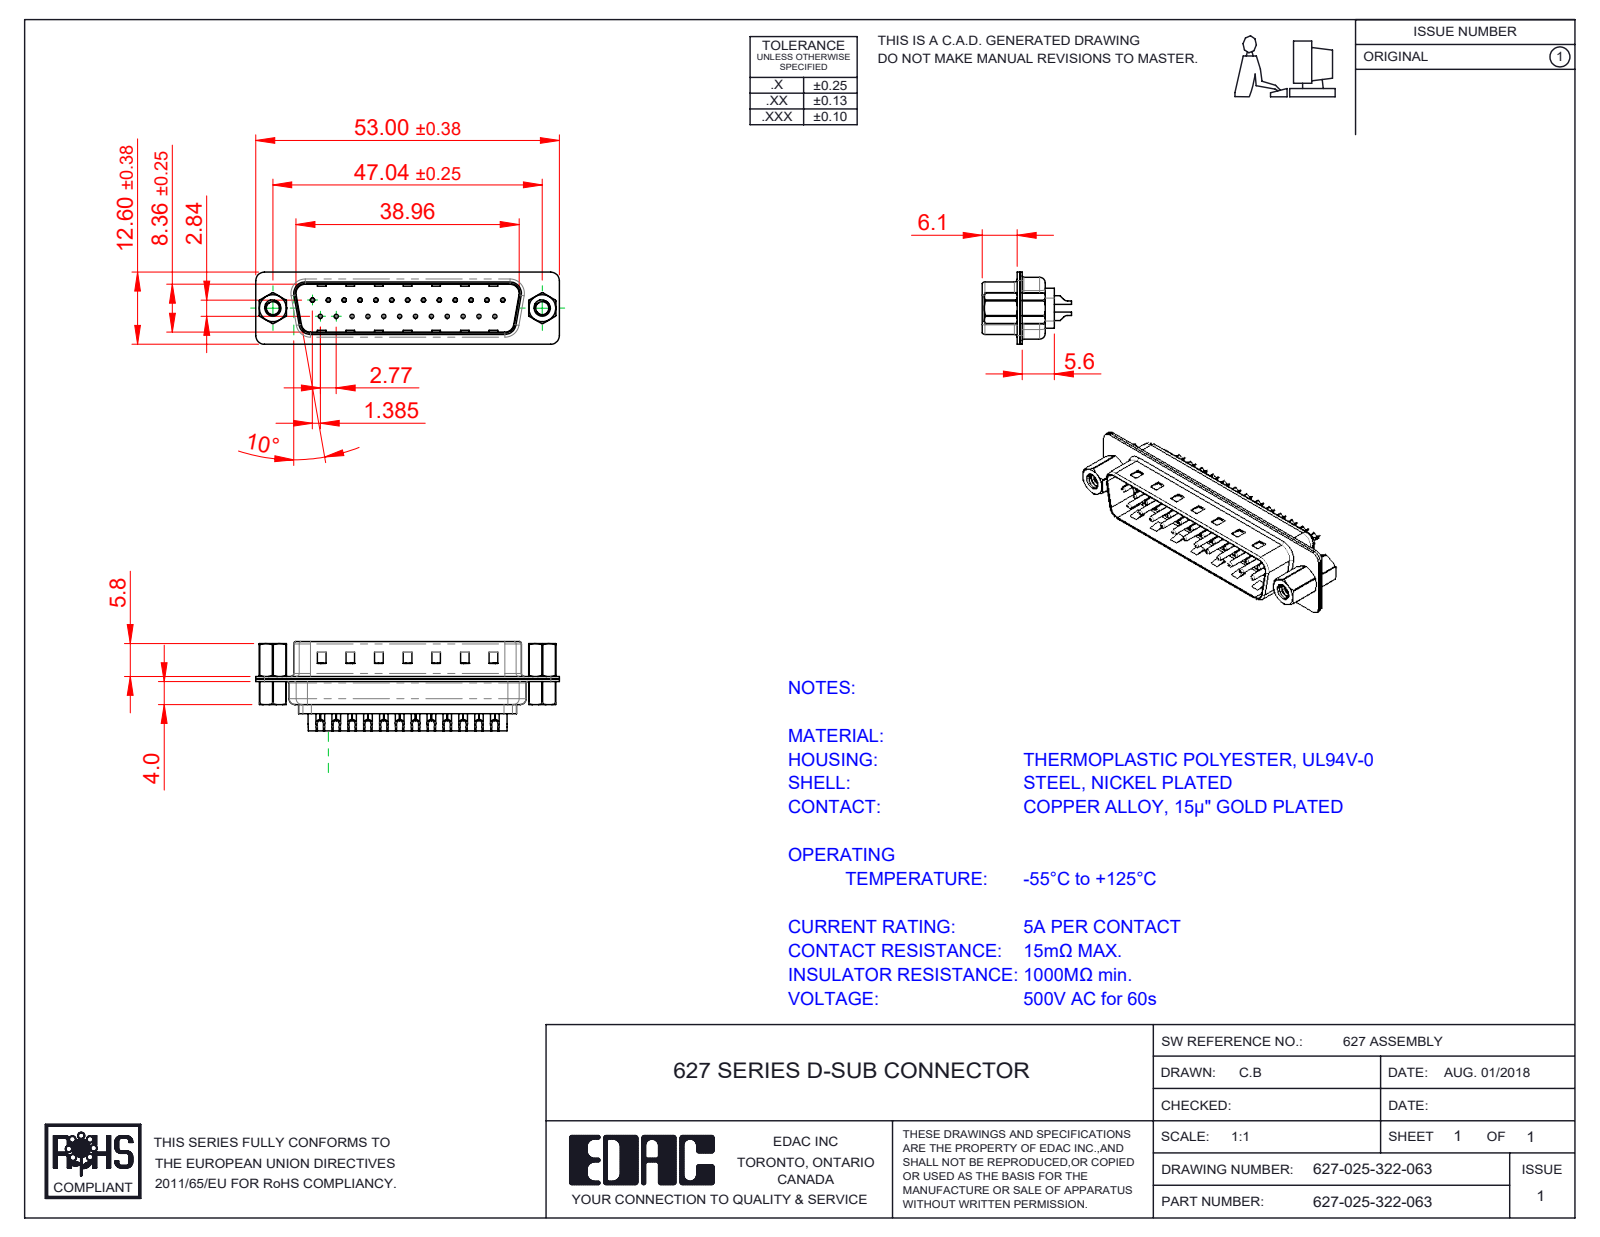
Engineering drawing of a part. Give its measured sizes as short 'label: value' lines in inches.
name: 627 Contact Row 1_22L; 627-025-322-063; 627 Contact Row 2_22L; 627 Housing_25 LP (+4 more)
written by: SolidWorks 2020 (CONFIG_CONTROL_DESIGN)
unit: in
bodies: 32 solids, 2098 faces (543 planar, 932 cylindrical, 623 other)
size: 2.087 × 0.604 × 0.496
volume: 0.177 in³; area: 12.91 in²
holes: 25× ⌀0.014, 25× ⌀0.043, 25× ⌀0.063, 2× ⌀0.089, 2× ⌀0.09, 2× ⌀0.157, 2× ⌀0.189
bosses: 25× ⌀0.079, 25× ⌀0.059, 25× ⌀0.03, 2× ⌀0.197, 2× ⌀0.193, 2× ⌀0.11
rounds: 16× R0.059, 12× R0.079, 8× R0.02, 8× R0.063, 6× R0.039, 4× R0.01, 4× R0.024, 4× R0.026
face distances: 0.016, 0.018, 0.032, 0.377, 0.345, 0.035, 0.059, 0.055, 0.256, 0.238
hole spacings: 0.124, 0.327, 0.109, 0.218, 0.436, 0.654, 0.198, 0.198
